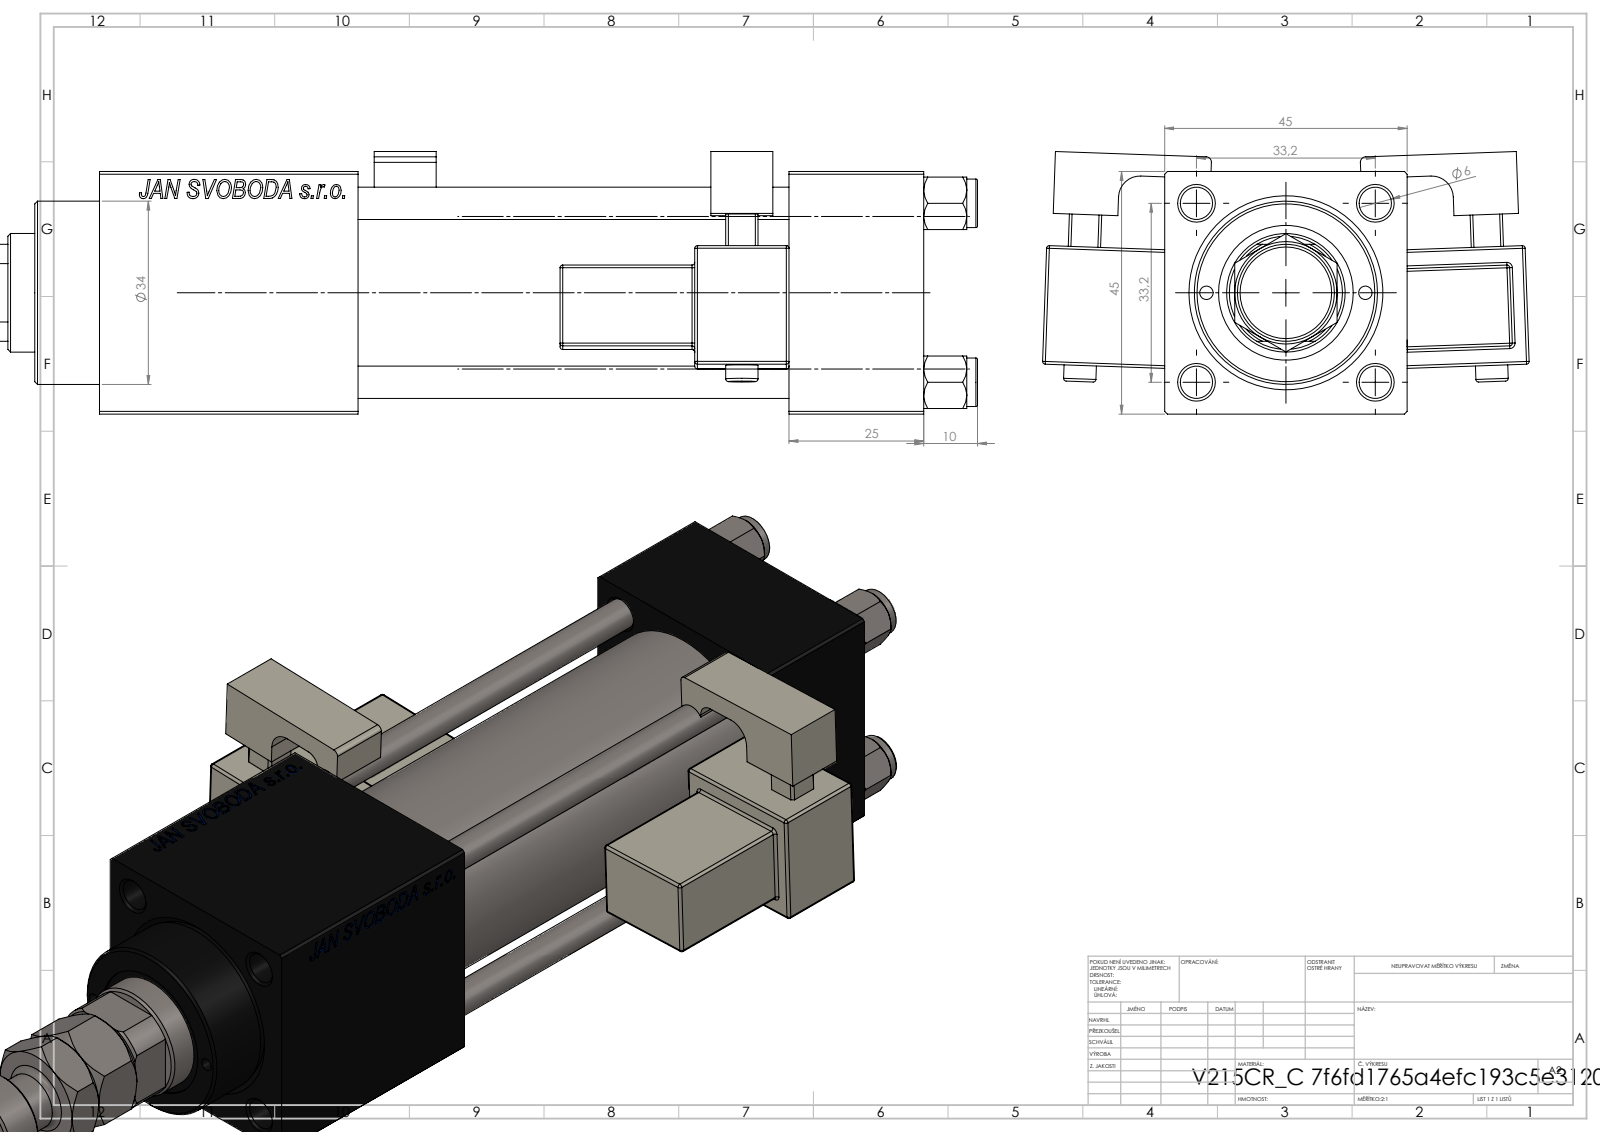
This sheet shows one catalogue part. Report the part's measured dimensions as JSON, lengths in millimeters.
{"part_name": "V215CR_VCP_C; MFA; V215CR_C_Body; NUT_M5_C (+3 more)", "step_written_by": "SolidWorks 2019 (CONFIG_CONTROL_DESIGN)", "units": "millimeters", "bodies": {"solids": 14, "faces": 1363, "planar": 605, "cylindrical": 154, "other": 604}, "overall_size": [221, 90.31, 48.72], "volume_mm3": 283111, "surface_area_mm2": 97200, "round_holes": [[6, 4], [2.5, 2], [7, 2], [13.16, 2], [20, 2], [10.5, 1], [22, 1], [24, 1], [25, 1], [32, 1], [33, 1]], "round_bosses_or_shafts": [[9, 4], [6, 2], [38, 1], [34, 1], [18, 1], [11, 1]], "partial_cylinders_radius": [[0.5, 48], [1, 2], [2.5, 2], [4, 2], [10.5, 1]], "face_to_face_distances": [45, 25, 3, 105, 80, 153, 22.99, 62.5, 48, 128], "hole_center_spacings": [16.7, 23.48, 33.2, 35.47, 14.75, 46.95, 29.5, 105.5]}
